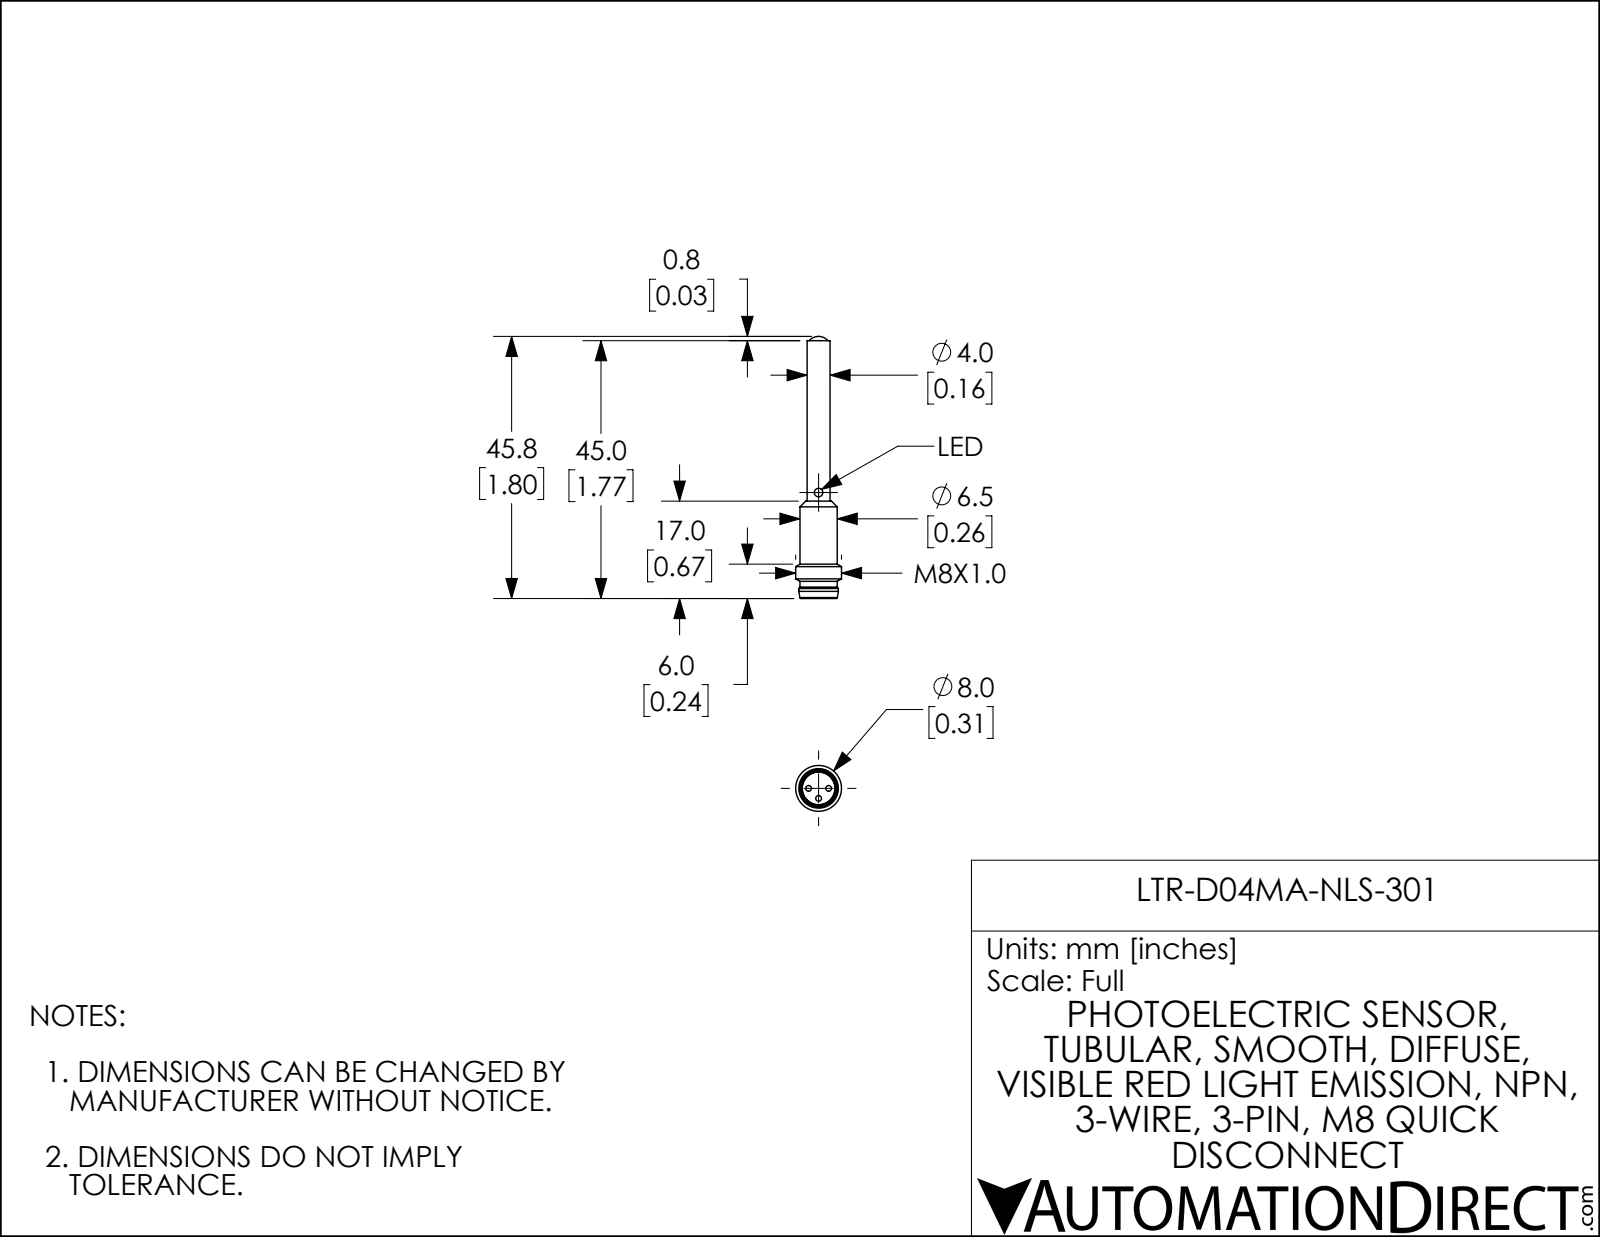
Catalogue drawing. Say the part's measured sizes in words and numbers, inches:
The part is named "LxR-D04MA-NxS". Its 3-D file was written by "SolidWorks 2018 (AUTOMOTIVE_DESIGN)". It is 1 solid with 28 faces: 5 planar, 12 cylindrical and 11 other. Overall it measures 1.801 by 0.315 by 0.315 inches. Its volume is 0.051 cubic inches and its surface area 1.43 square inches. Round holes: 1 of diameter 0.059, 1 of diameter 0.228. Round bosses or shafts: 3 of diameter 0.039, 1 of diameter 0.315, 1 of diameter 0.272, 1 of diameter 0.256, 1 of diameter 0.224, 1 of diameter 0.157. Partial cylindrical surfaces (rounded edges, fillets, slot ends): 1 of radius 0.07. The main face-to-face distances are 1.578, 0.476, 1.102, 0.193, 0.669, 1.772, 0.197, 0.472, 1.575.
